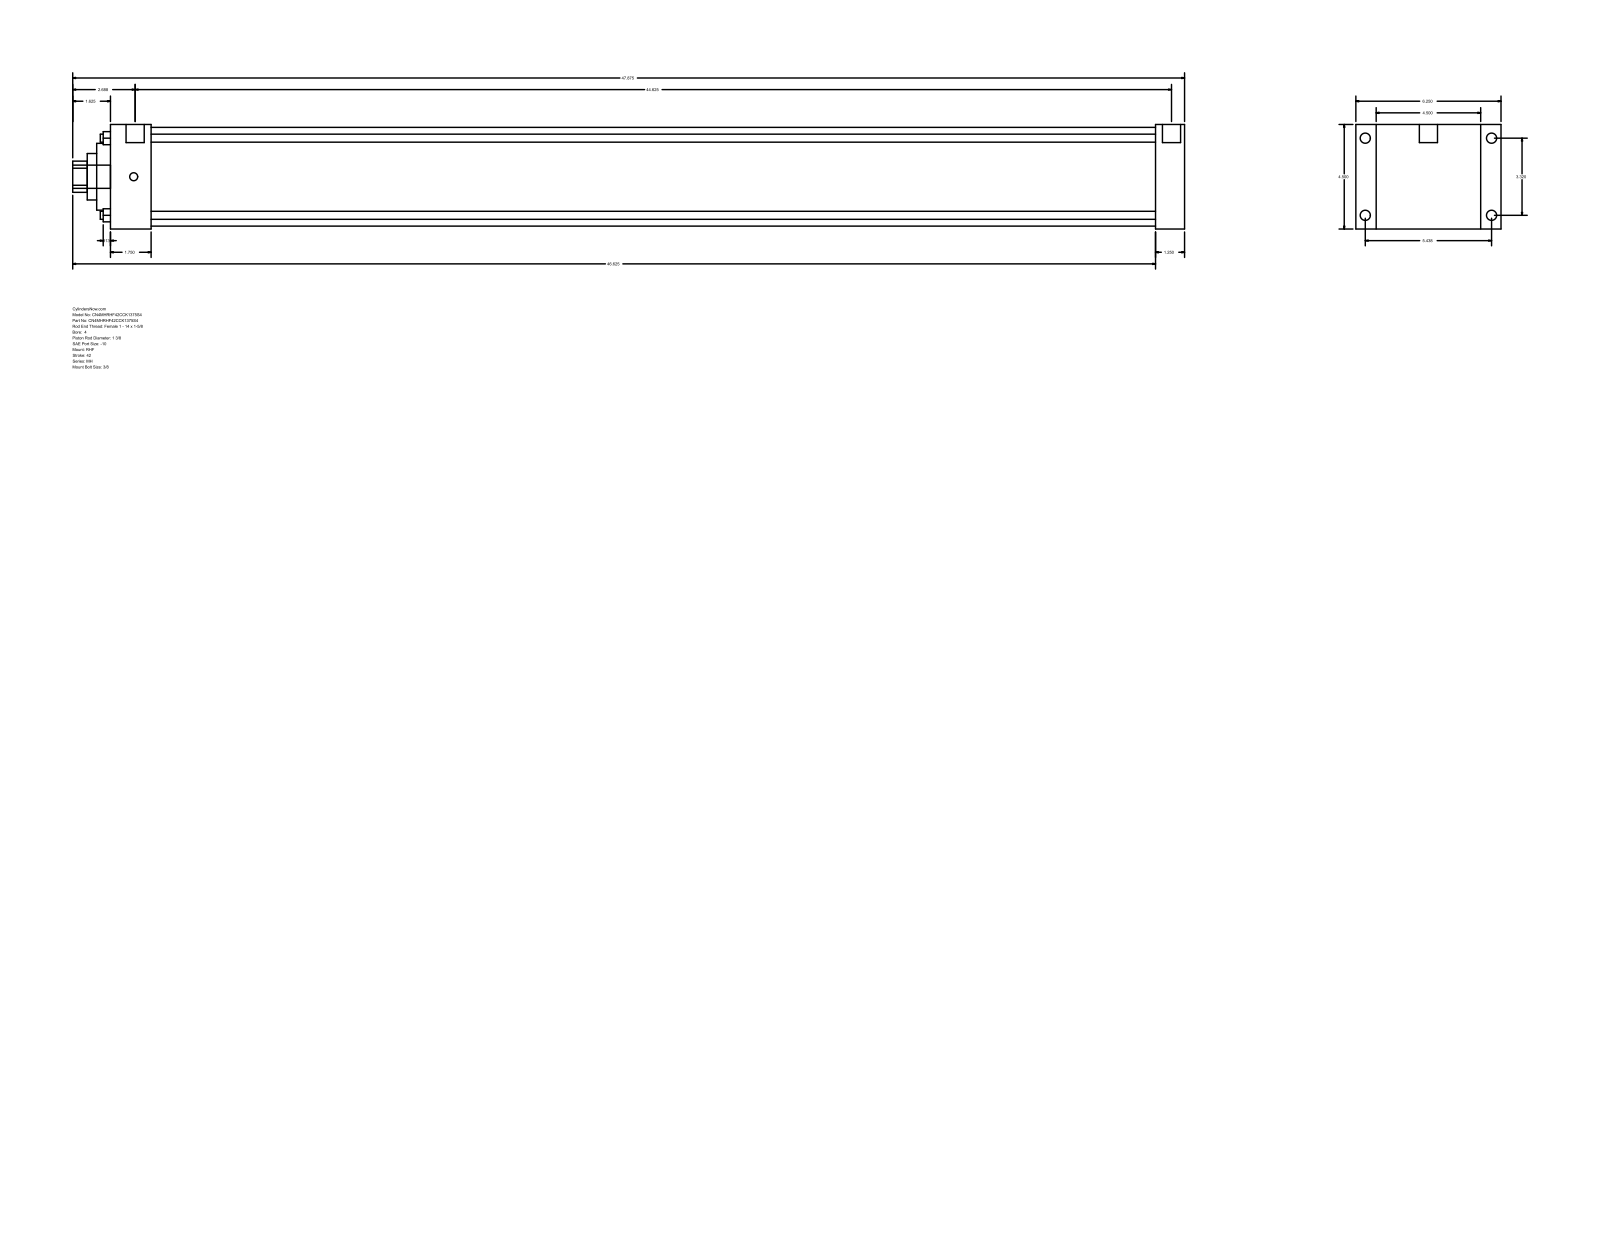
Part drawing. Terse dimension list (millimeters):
name: MH_RHF__0400_1.375
written by: GSSL Pune (CONFIG_CONTROL_DESIGN)
unit: mm
bodies: 0 solids, 90 faces (61 planar, 29 cylindrical, 0 other)
size: 1216.03 × 158.75 × 114.3
holes: 4× ⌀8.76, 1× ⌀34.92, 1× ⌀50.8, 1× ⌀73.03, 1× ⌀107.95
bosses: 4× ⌀11.13, 4× ⌀8.73, 2× ⌀19.84, 1× ⌀25.4
rounds: 1× R17.06
face distances: 114.3, 1174.76, 1143.01, 31.75, 22.23, 136.53, 44.45, 1098.56, 1130.31, 158.76
hole spacings: 59.62, 84.32, 119.25
